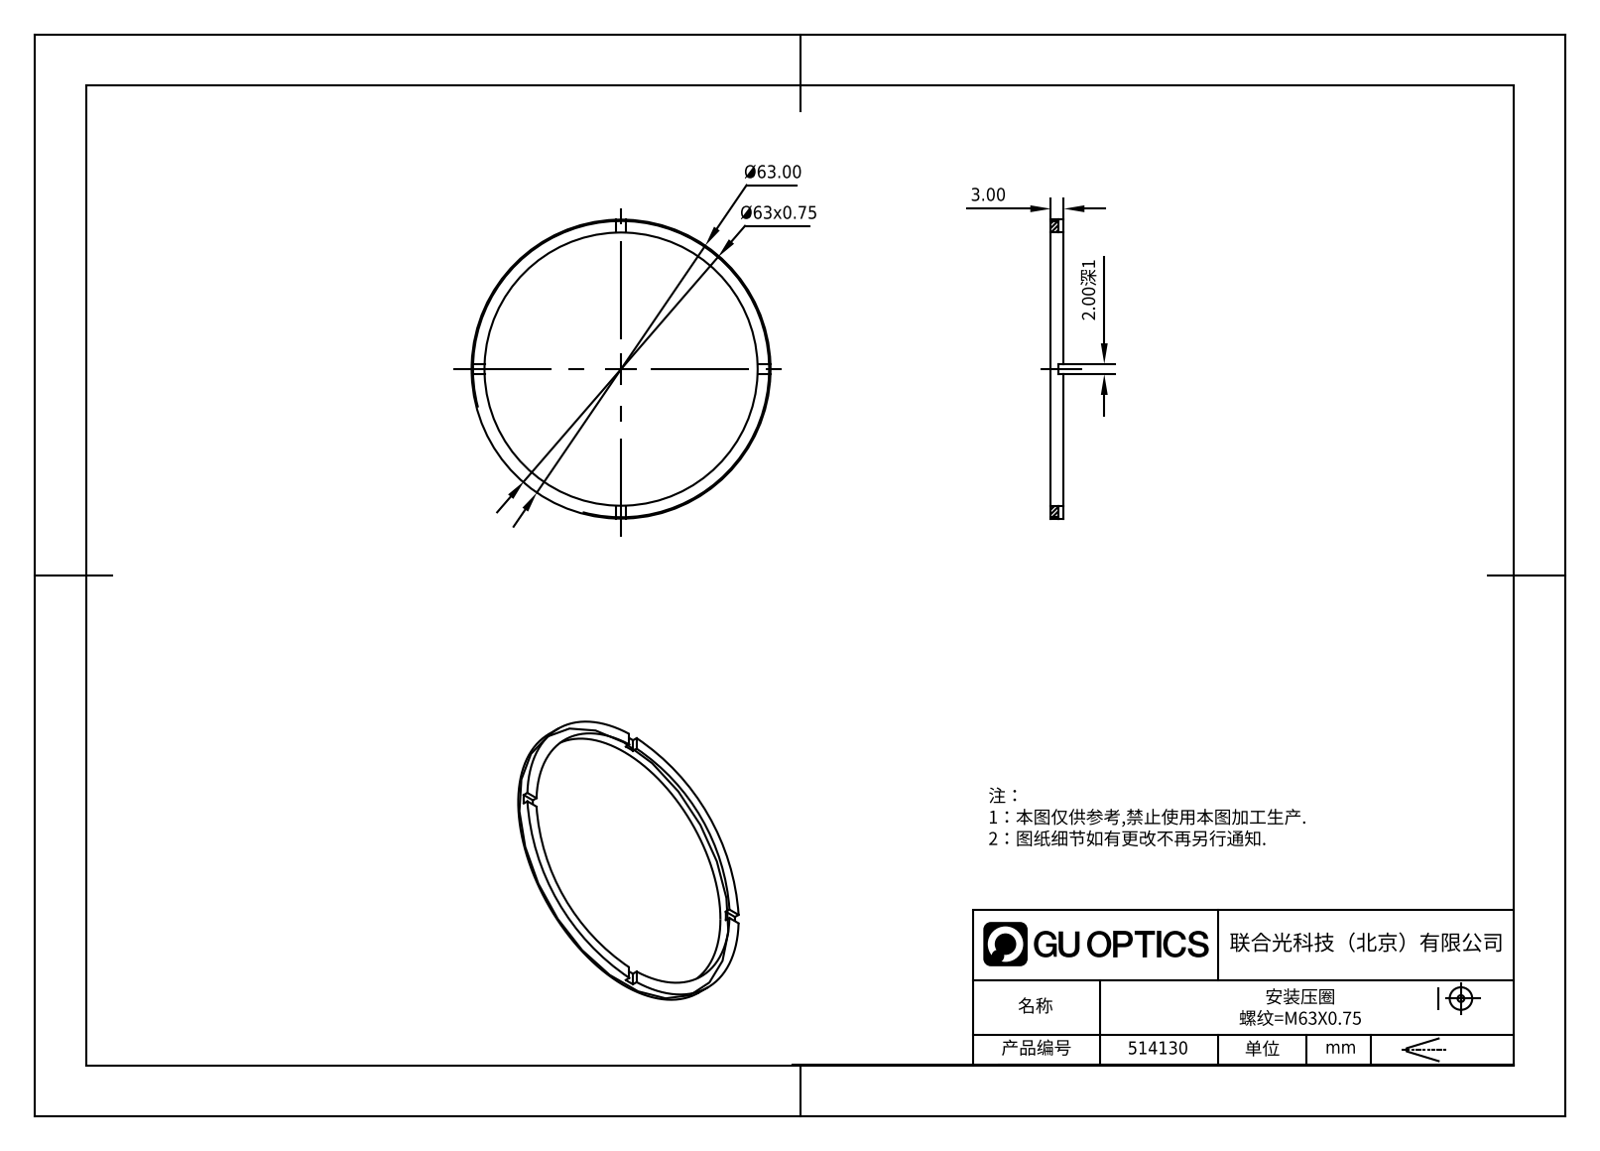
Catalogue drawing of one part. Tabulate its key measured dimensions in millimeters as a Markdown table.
| quantity | value |
| --- | --- |
| part name | 514130 |
| STEP written by | SolidWorks 2020 (CONFIG_CONTROL_DESIGN) |
| units | millimeters |
| bodies | 1 solid, 21 faces (17 planar, 4 cylindrical, 0 other) |
| overall size | 63 × 63 × 3 |
| volume | 1 405 mm³ |
| surface area | 2 095 mm² |
| round holes (diameter × count) | 58 × 1 |
| round bosses / shafts (diameter × count) | 63 × 1 |
| main face-to-face distances | 3, 2, 1 |
